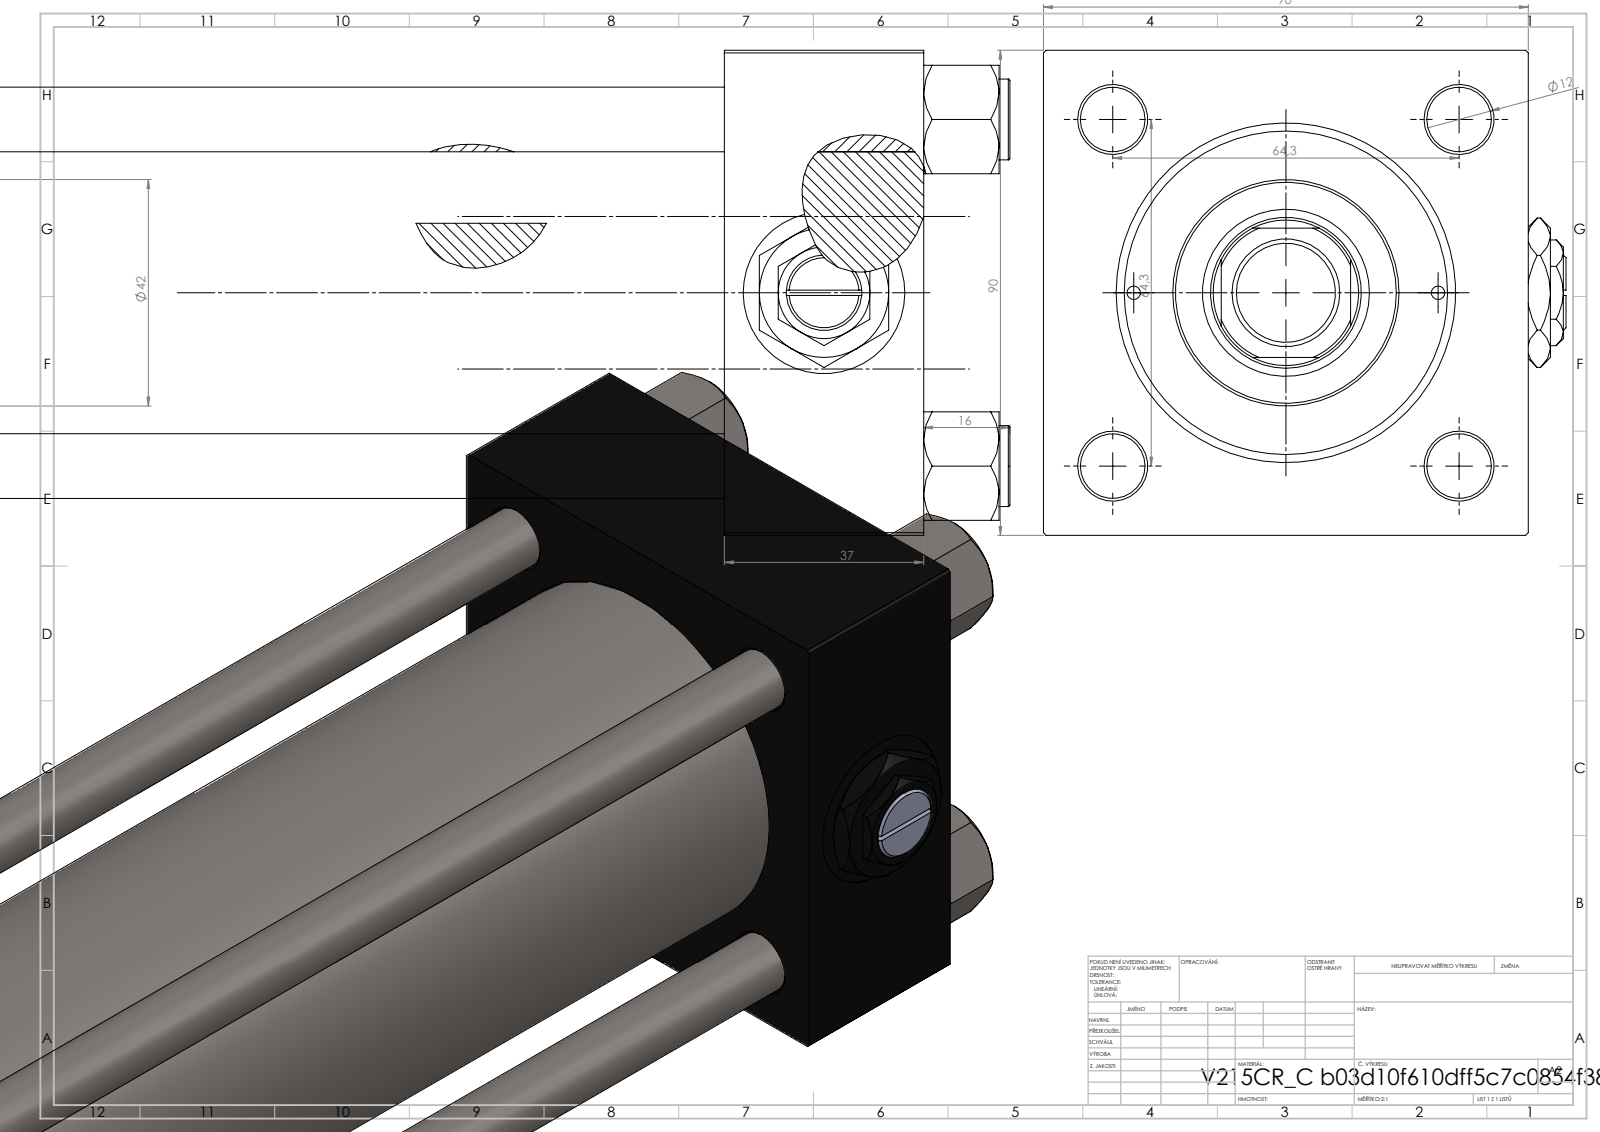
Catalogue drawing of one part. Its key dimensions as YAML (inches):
part_name: "V215_VC_A; V215CR_C_Body; V215CR_VCP_C; Zatka_pro_OIL_PORT (+3 more)"
step_written_by: "SolidWorks 2019 (CONFIG_CONTROL_DESIGN)"
units: inches
bodies: {solids: 14, faces: 1270, planar: 580, cylindrical: 106, other: 584}
overall_size: [18.15, 3.819, 3.543]
volume: 81.65
surface_area: 521.9
round_holes:
  - {diameter: 0.472, count: 4}
  - {diameter: 0.098, count: 2}
  - {diameter: 0.276, count: 2}
  - {diameter: 0.825, count: 2}
  - {diameter: 1.181, count: 2}
  - {diameter: 0.728, count: 1}
  - {diameter: 1.102, count: 1}
  - {diameter: 1.22, count: 1}
  - {diameter: 1.969, count: 1}
  - {diameter: 2.362, count: 1}
  - {diameter: 2.48, count: 1}
round_bosses_or_shafts:
  - {diameter: 0.591, count: 4}
  - {diameter: 2.717, count: 1}
  - {diameter: 1.654, count: 1}
  - {diameter: 0.787, count: 1}
  - {diameter: 0.709, count: 1}
partial_cylinders:
  - {radius: 0.531, count: 1}
face_to_face_distances: [3.543, 1.457, 13.701, 15.157, 2.323, 12.835, 11.378, 14.028, 12.571, 1.193]
hole_center_spacings: [1.275, 1.79, 2.531, 2.694, 1.112, 3.58, 2.224, 12.894]
